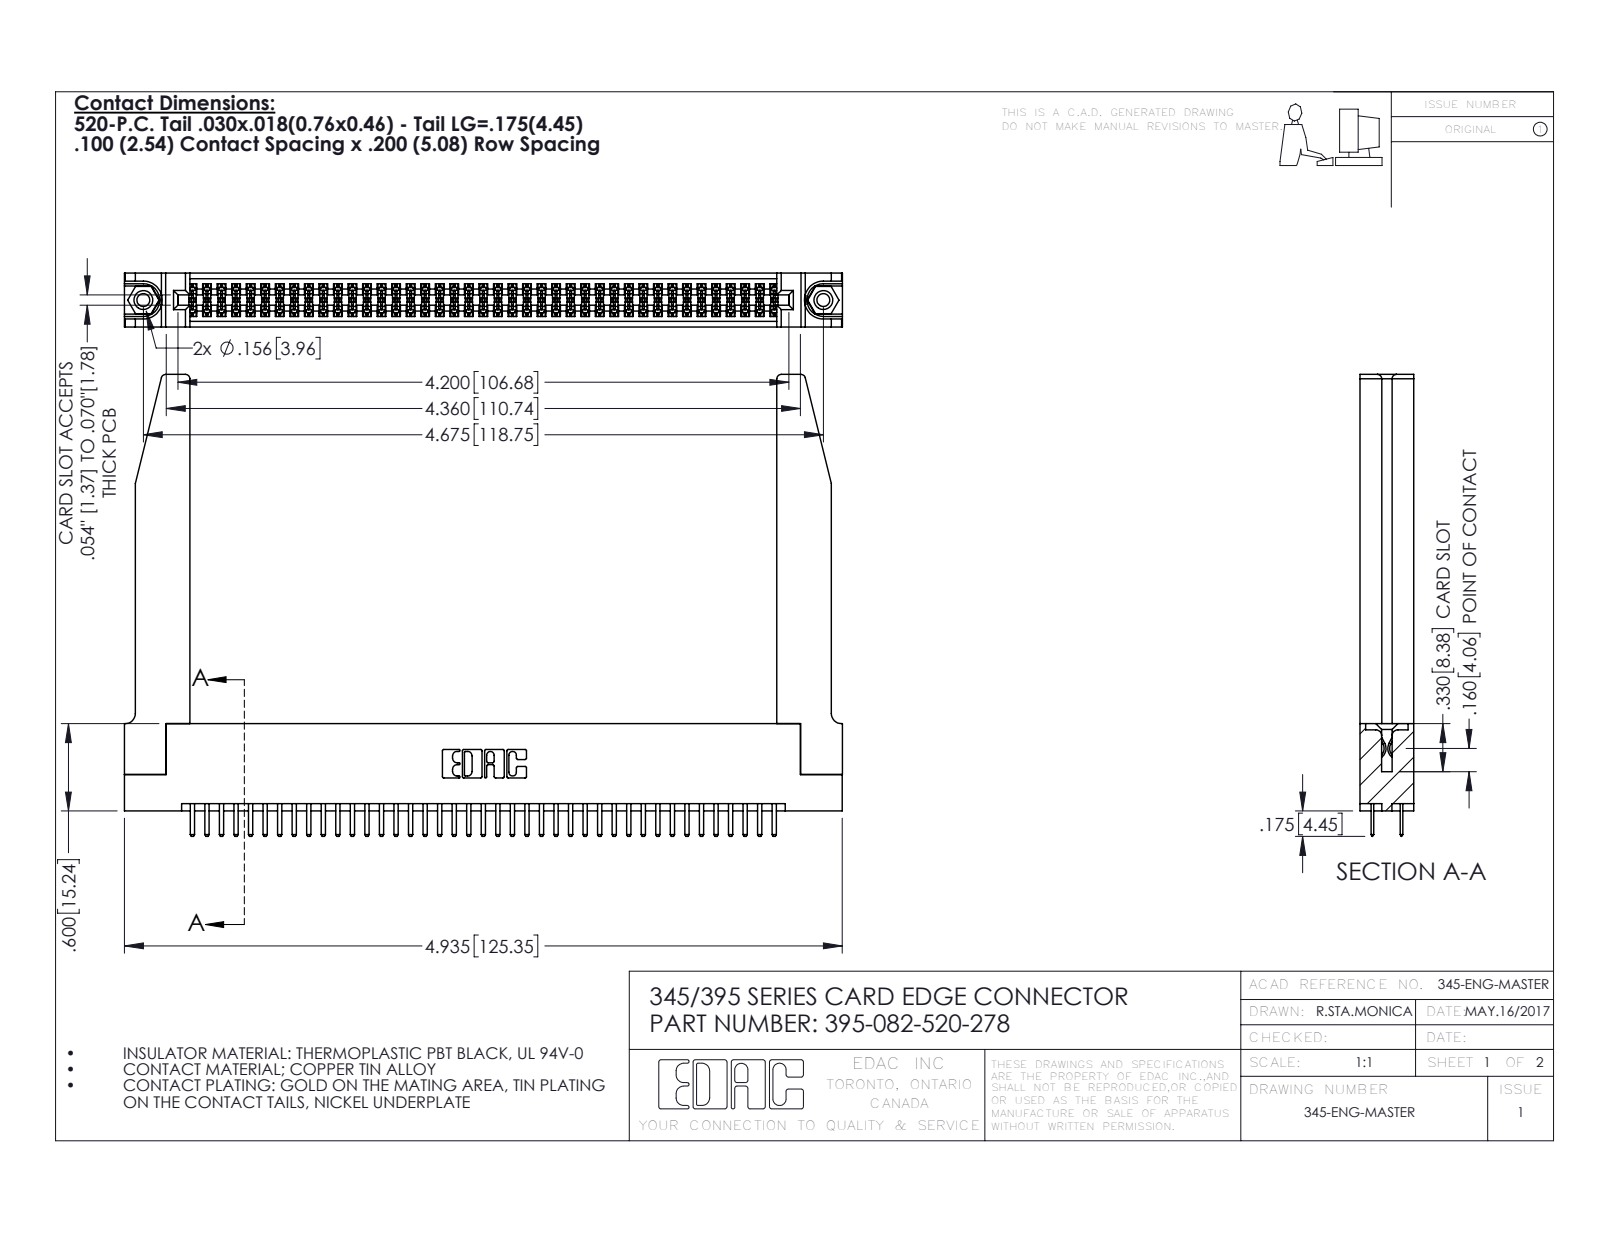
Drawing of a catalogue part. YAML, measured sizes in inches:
part_name: "345-250-001_345-250-001-102; 395-082-520-278; 345-292-001_345-293-120; 345 Part_Flush Mounting Lugs - 0.156 Dia-TH (+1 more)"
step_written_by: "SolidWorks 2016 (CONFIG_CONTROL_DESIGN)"
units: inches
bodies: {solids: 87, faces: 4788, planar: 3092, cylindrical: 1644, other: 52}
overall_size: [4.936, 3.175, 0.37]
volume: 1.215
surface_area: 38.25
round_holes:
  - {diameter: 0.089, count: 2}
  - {diameter: 0.125, count: 2}
  - {diameter: 0.156, count: 2}
  - {diameter: 0.064, count: 1}
round_bosses_or_shafts:
  - {diameter: 0.155, count: 2}
partial_cylinders:
  - {radius: 0.006, count: 123}
  - {radius: 0.01, count: 86}
  - {radius: 0.01, count: 22}
  - {radius: 0.03, count: 8}
  - {radius: 0.007, count: 6}
  - {radius: 0.031, count: 6}
  - {radius: 0.026, count: 3}
  - {radius: 0.014, count: 2}
face_to_face_distances: [0.37, 0.072, 0.298, 0.2, 0.098, 0.272, 0.025, 0.225, 0.022, 0.175]
hole_center_spacings: [0.27, 4.439, 4.675]
